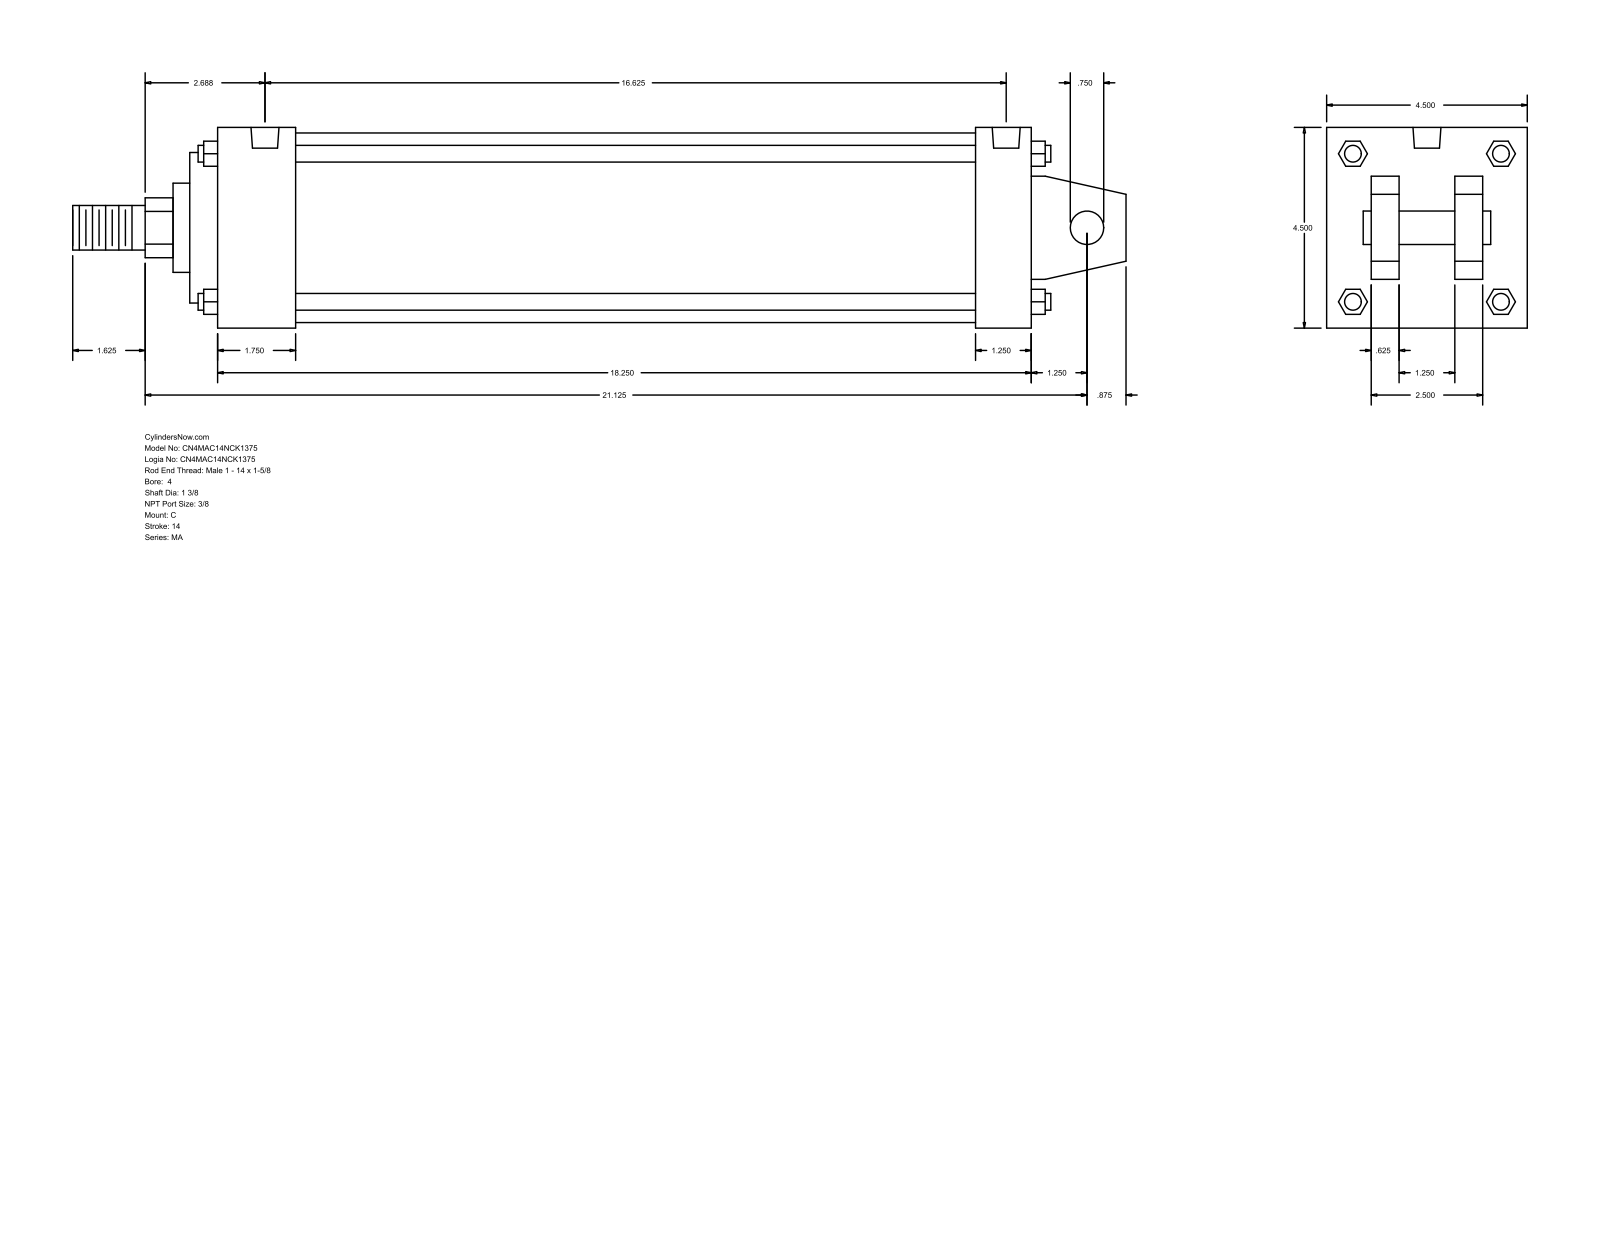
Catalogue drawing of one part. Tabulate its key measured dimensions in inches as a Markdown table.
| quantity | value |
| --- | --- |
| part name | MA_C__0400_1.375 |
| STEP written by | GSSL Pune (CONFIG_CONTROL_DESIGN) |
| units | inches |
| bodies | 0 solids, 141 faces (109 planar, 32 cylindrical, 0 other) |
| overall size | 23.625 × 4.5 × 4.5 |
| round holes (diameter × count) | 0.437 × 4, 0.627 × 2 |
| round bosses / shafts (diameter × count) | 0.375 × 4, 4.25 × 1, 3.375 × 1, 2 × 1, 1.375 × 1, 1 × 1, 0.75 × 1 |
| partial cylindrical surfaces (radius × count) | 0.672 × 1 |
| main face-to-face distances | 4.5, 0.625, 18.25, 2.875, 1.625, 1, 3.5, 1.875, 18.875, 17.625 |
| hole center spacings | 0.188, 16.25, 16.437, 16.625 |
